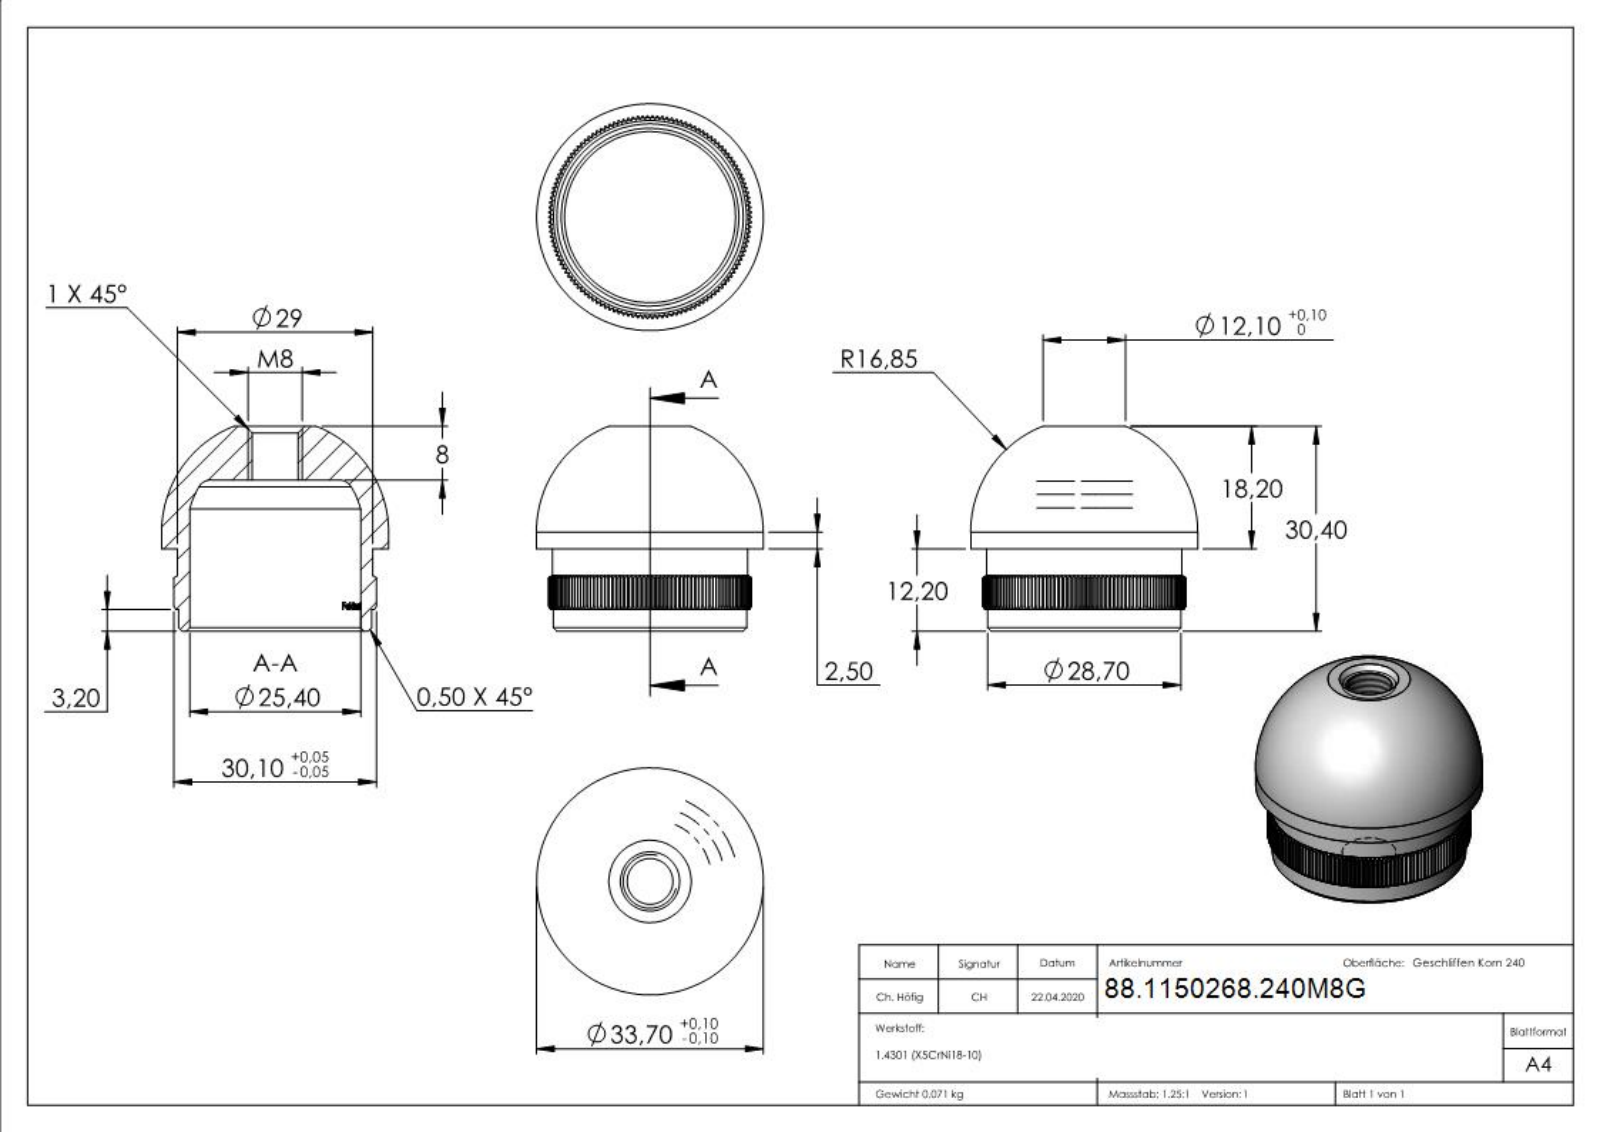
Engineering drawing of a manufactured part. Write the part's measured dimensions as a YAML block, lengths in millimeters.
part_name: "50268-240M8G"
step_written_by: "SolidWorks 2015 (CONFIG_CONTROL_DESIGN)"
units: millimeters
bodies: {solids: 1, faces: 1005, planar: 411, cylindrical: 187, other: 407}
overall_size: [33.7, 33.7, 30.4]
volume: 8913
surface_area: 6239
round_holes:
  - {diameter: 6.8, count: 1}
  - {diameter: 25.4, count: 1}
round_bosses_or_shafts:
  - {diameter: 33.7, count: 1}
  - {diameter: 28.7, count: 1}
partial_cylinders:
  - {radius: 12.8, count: 1}
  - {radius: 15.05, count: 1}
face_to_face_distances: [14.55, 10.2, 14.54, 14.56, 12.2, 22.4, 8, 30.4, 18.2, 3.2]
